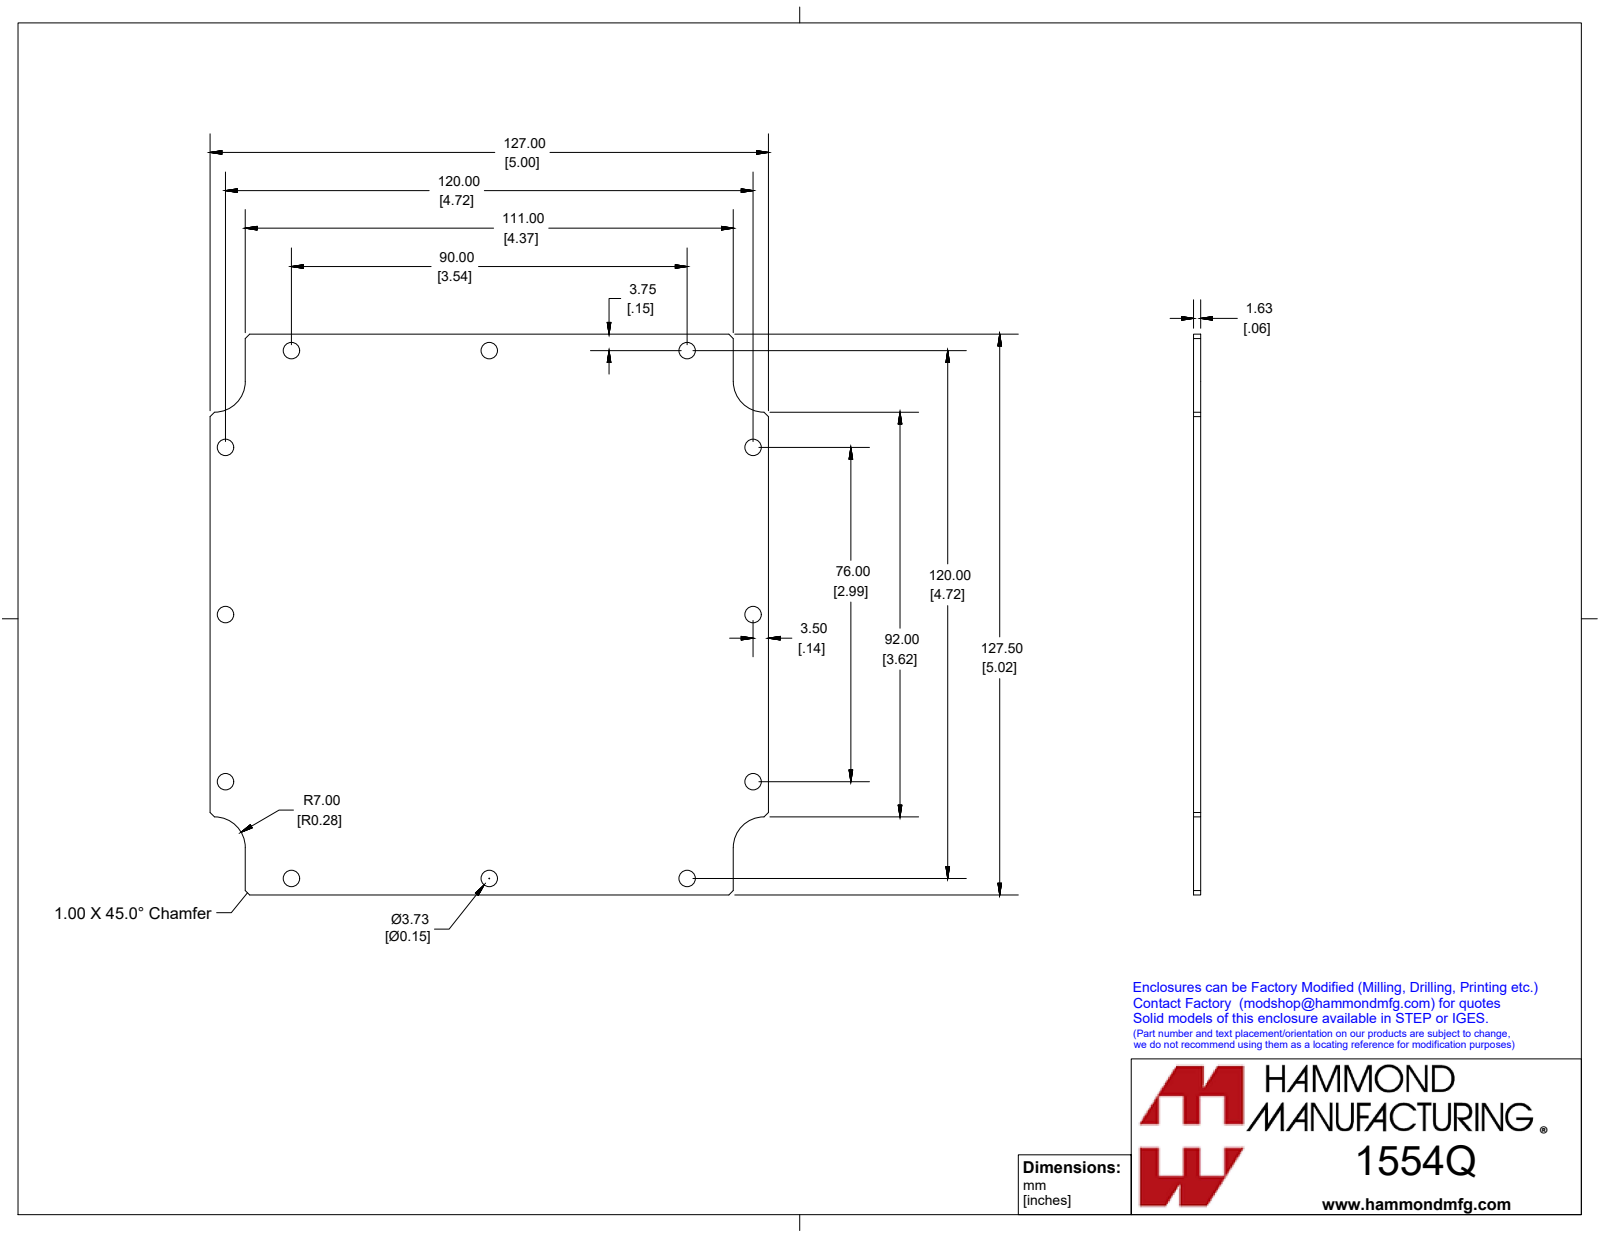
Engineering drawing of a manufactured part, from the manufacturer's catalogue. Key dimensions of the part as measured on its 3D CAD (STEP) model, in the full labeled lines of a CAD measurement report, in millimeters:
Part name (STEP PRODUCT): 1554QPL
STEP written by: SolidWorks 2019 (CONFIG_CONTROL_DESIGN)
Units: millimetres
Bodies: 1 solid, 34 faces (18 planar, 16 cylindrical, 0 other)
Overall size (bounding box): 127.5 × 127 × 1.6
Volume: 25 250 mm³ · Surface area: 32 090 mm²
Round holes (diameter × count): ⌀3.7 ×12
Partial cylindrical surfaces — rounded edges, fillets, slot ends (radius × count): R7 ×4
Main face-to-face distances: 1.6, 127.5, 127, 8, 119, 111, 6.9, 160.3, 153.4, 167.2
Hole centre spacings: 120, 26.6, 38, 45, 61.8, 63.9, 84.9, 99.1
